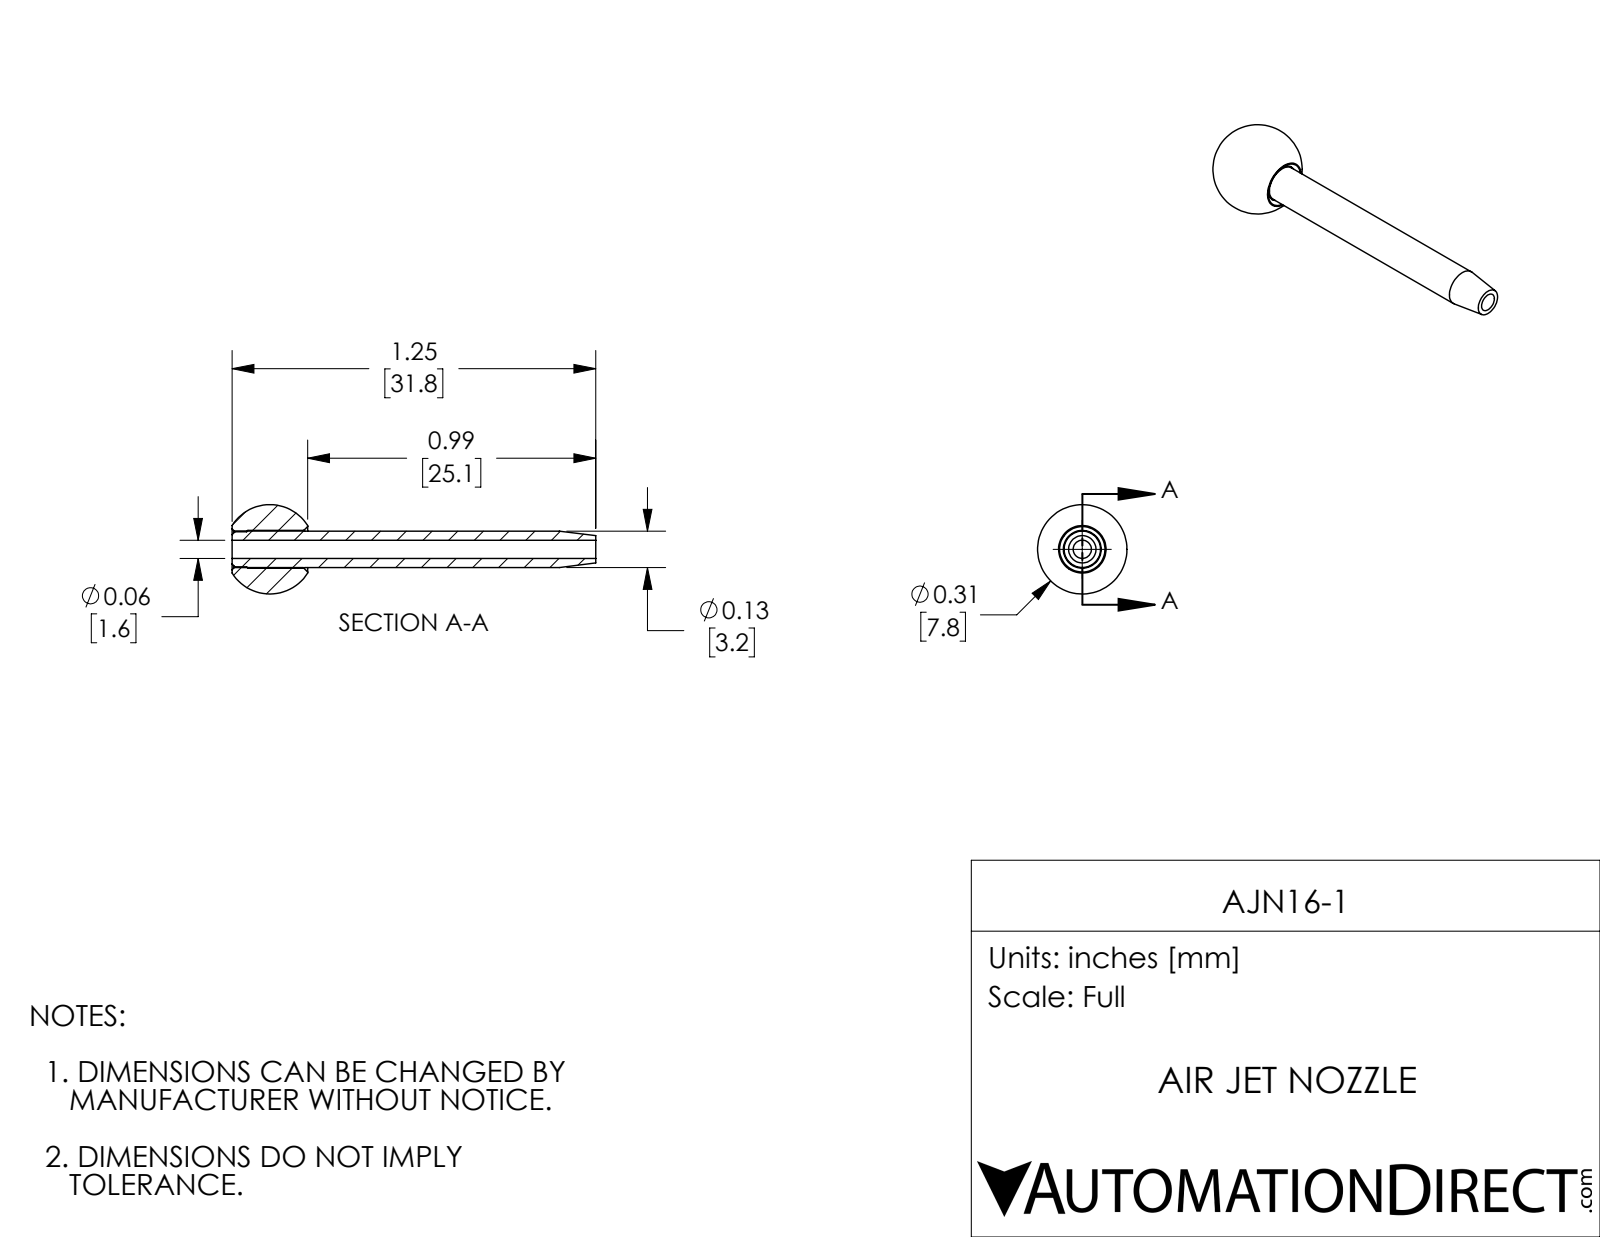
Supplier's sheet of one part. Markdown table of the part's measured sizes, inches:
| quantity | value |
| --- | --- |
| part name | AJN16-1 |
| STEP written by | SolidWorks 2018 (AUTOMOTIVE_DESIGN) |
| units | inches |
| bodies | 2 solids, 28 faces (4 planar, 10 cylindrical, 14 other) |
| overall size | 1.25 × 0.307 × 0.307 |
| volume | 0.023 in³ |
| surface area | 1.11 in² |
| round holes (diameter × count) | 0.063 × 1, 0.126 × 1 |
| round bosses / shafts (diameter × count) | 0.13 × 1, 0.125 × 1, 0.121 × 1 |
| main face-to-face distances | 1.25, 0.26, 0.99 |
